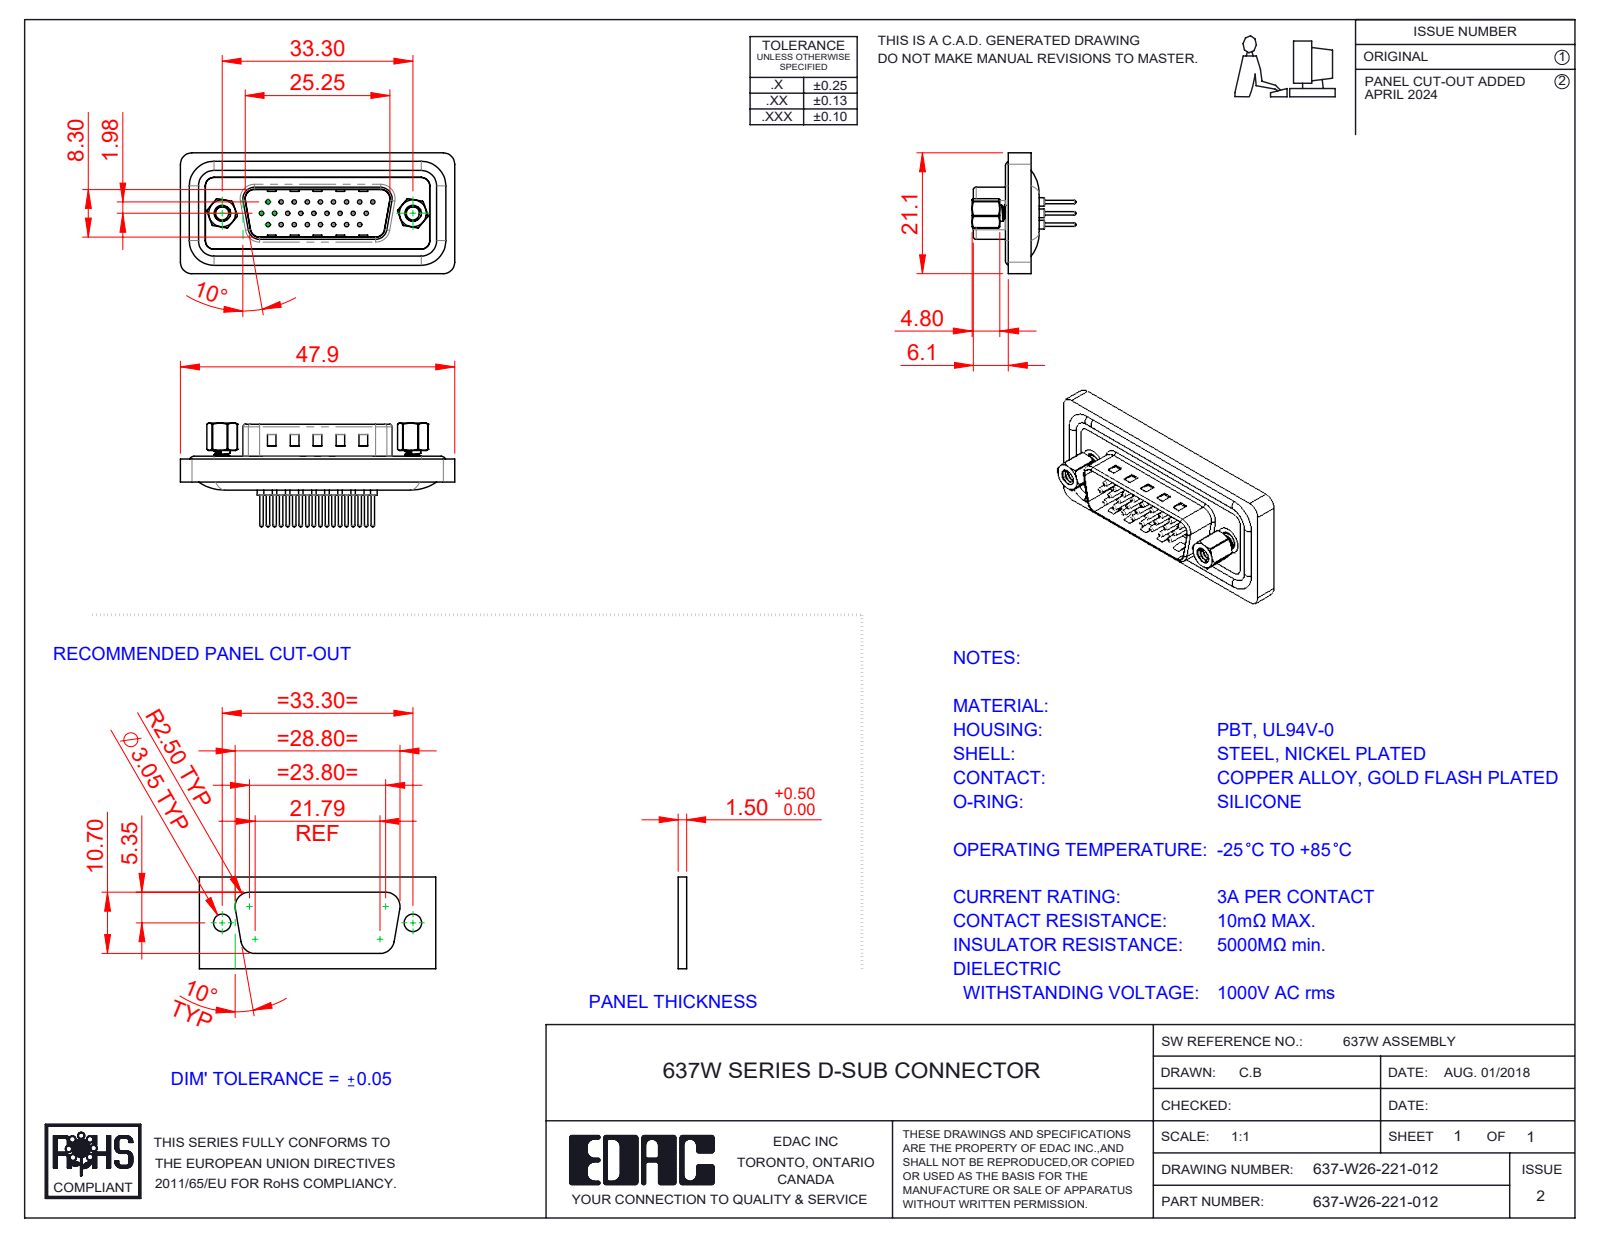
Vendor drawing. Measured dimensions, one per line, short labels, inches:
name: 637W Contact Row 2_21; 637W Contact Row 1_21; 637W Shell_26 Contacts; 637W Housing_26 Contacts (+5 more)
written by: SolidWorks 2016 (CONFIG_CONTROL_DESIGN)
unit: in
bodies: 34 solids, 1496 faces (355 planar, 628 cylindrical, 513 other)
size: 1.885 × 0.831 × 0.705
volume: 0.299 in³; area: 13.63 in²
holes: 26× ⌀0.03, 26× ⌀0.059, 26× ⌀0.063, 26× ⌀0.079, 2× ⌀0.089, 2× ⌀0.09, 2× ⌀0.157, 2× ⌀0.189, 2× ⌀0.197
bosses: 26× ⌀0.059, 26× ⌀0.024, 4× ⌀0.063, 2× ⌀0.193, 2× ⌀0.11, 1× ⌀0.197
rounds: 16× R0.079, 14× R0.059, 8× R0.02, 6× R0.106, 4× R0.035, 4× R0.063, 4× R0.169, 2× R0.016
face distances: 0.016, 0.063, 0.043, 0.114, 0.098, 0.02, 0.222, 0.608, 0.03, 0.134
hole spacings: 0.156, 0.09, 0.18, 0.238, 0.09, 0.324, 0.27, 0.238
